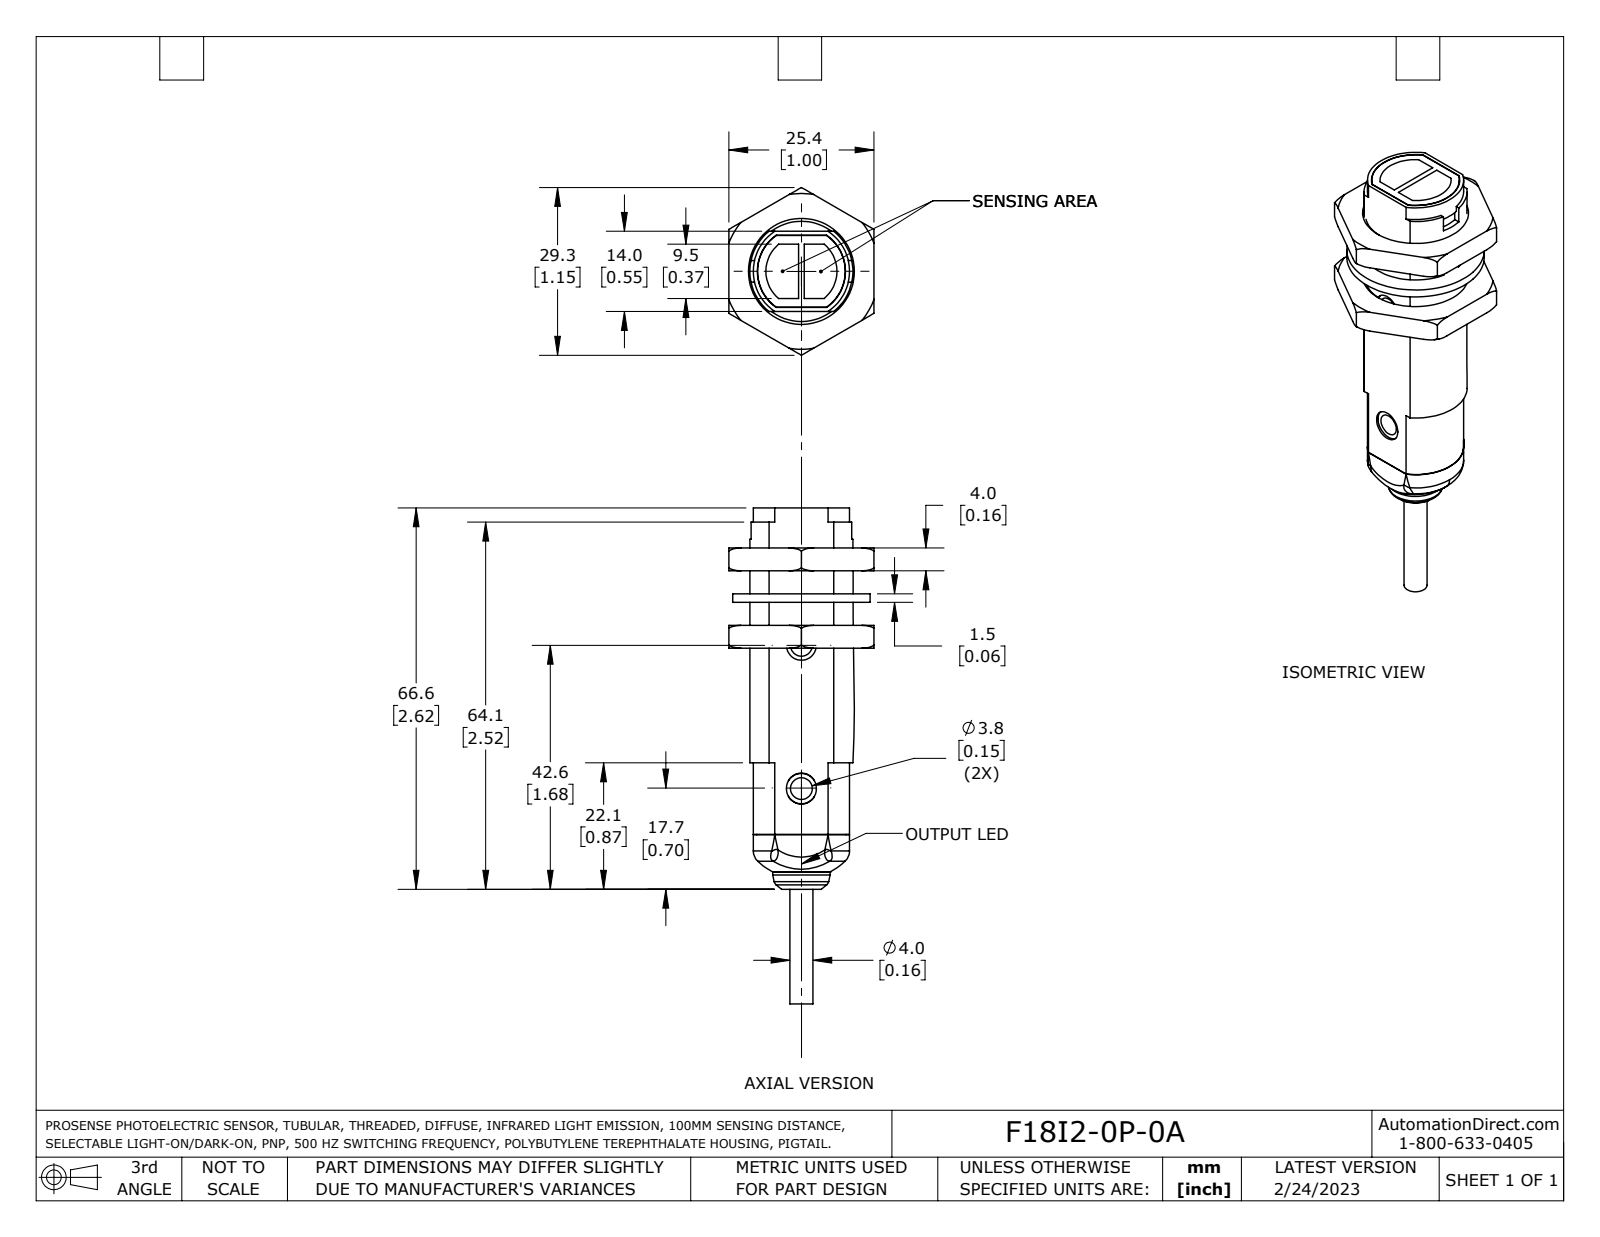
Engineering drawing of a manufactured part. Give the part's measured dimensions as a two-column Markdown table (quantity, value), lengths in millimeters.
| quantity | value |
| --- | --- |
| part name | F18I2-0N-0A |
| STEP written by | SolidWorks 2021 (AUTOMOTIVE_DESIGN) |
| units | millimeters |
| bodies | 4 solids, 158 faces (67 planar, 43 cylindrical, 48 other) |
| overall size | 86.58 × 29.28 × 25.36 |
| volume | 16 524 mm³ |
| surface area | 7 492 mm² |
| round holes (diameter × count) | 3.8 × 2, 5.2 × 1, 17.5 × 1, 18 × 1 |
| round bosses / shafts (diameter × count) | 24 × 1, 10 × 1, 4 × 1 |
| partial cylindrical surfaces (radius × count) | 1 × 4, 1.5 × 4, 2.6 × 2, 28 × 2, 2.65 × 1, 7.65 × 1, 7.7 × 1, 7.8 × 1 |
| main face-to-face distances | 4, 9.5, 14, 13.5, 5.5, 8, 25.36, 17.5, 11, 1.5 |
| hole center spacings | 25 |
